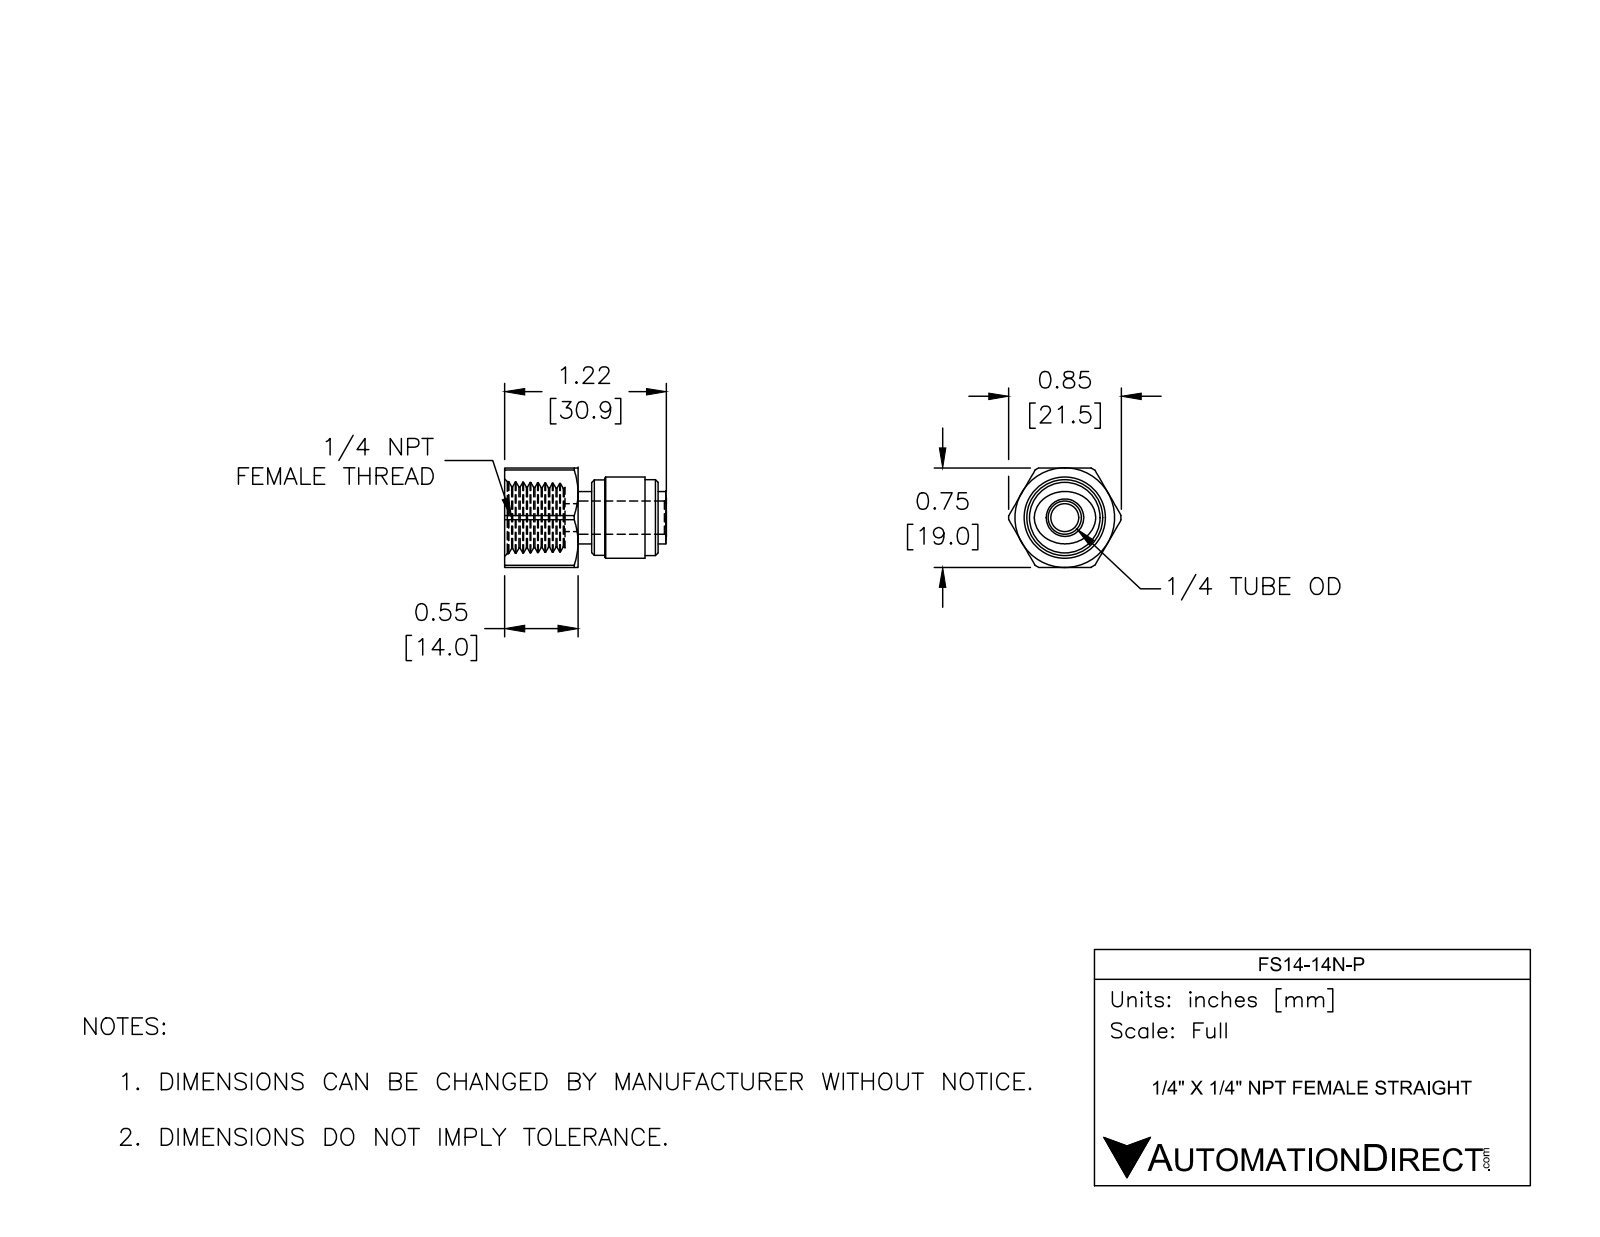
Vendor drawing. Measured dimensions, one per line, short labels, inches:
name: FS14-14N-P
written by: SolidWorks 2017 (AUTOMOTIVE_DESIGN)
unit: in
bodies: 1 solid, 134 faces (14 planar, 19 cylindrical, 101 other)
size: 1.217 × 0.846 × 0.748
volume: 0.303 in³; area: 5.432 in²
holes: 1× ⌀0.209, 1× ⌀0.25
bosses: 1× ⌀0.61, 1× ⌀0.571, 1× ⌀0.567, 1× ⌀0.394
rounds: 1× R0.423
face distances: 0.748, 0.551, 0.098, 0.453, 0.201, 0.602, 0.654, 0.102, 1.154, 0.701
